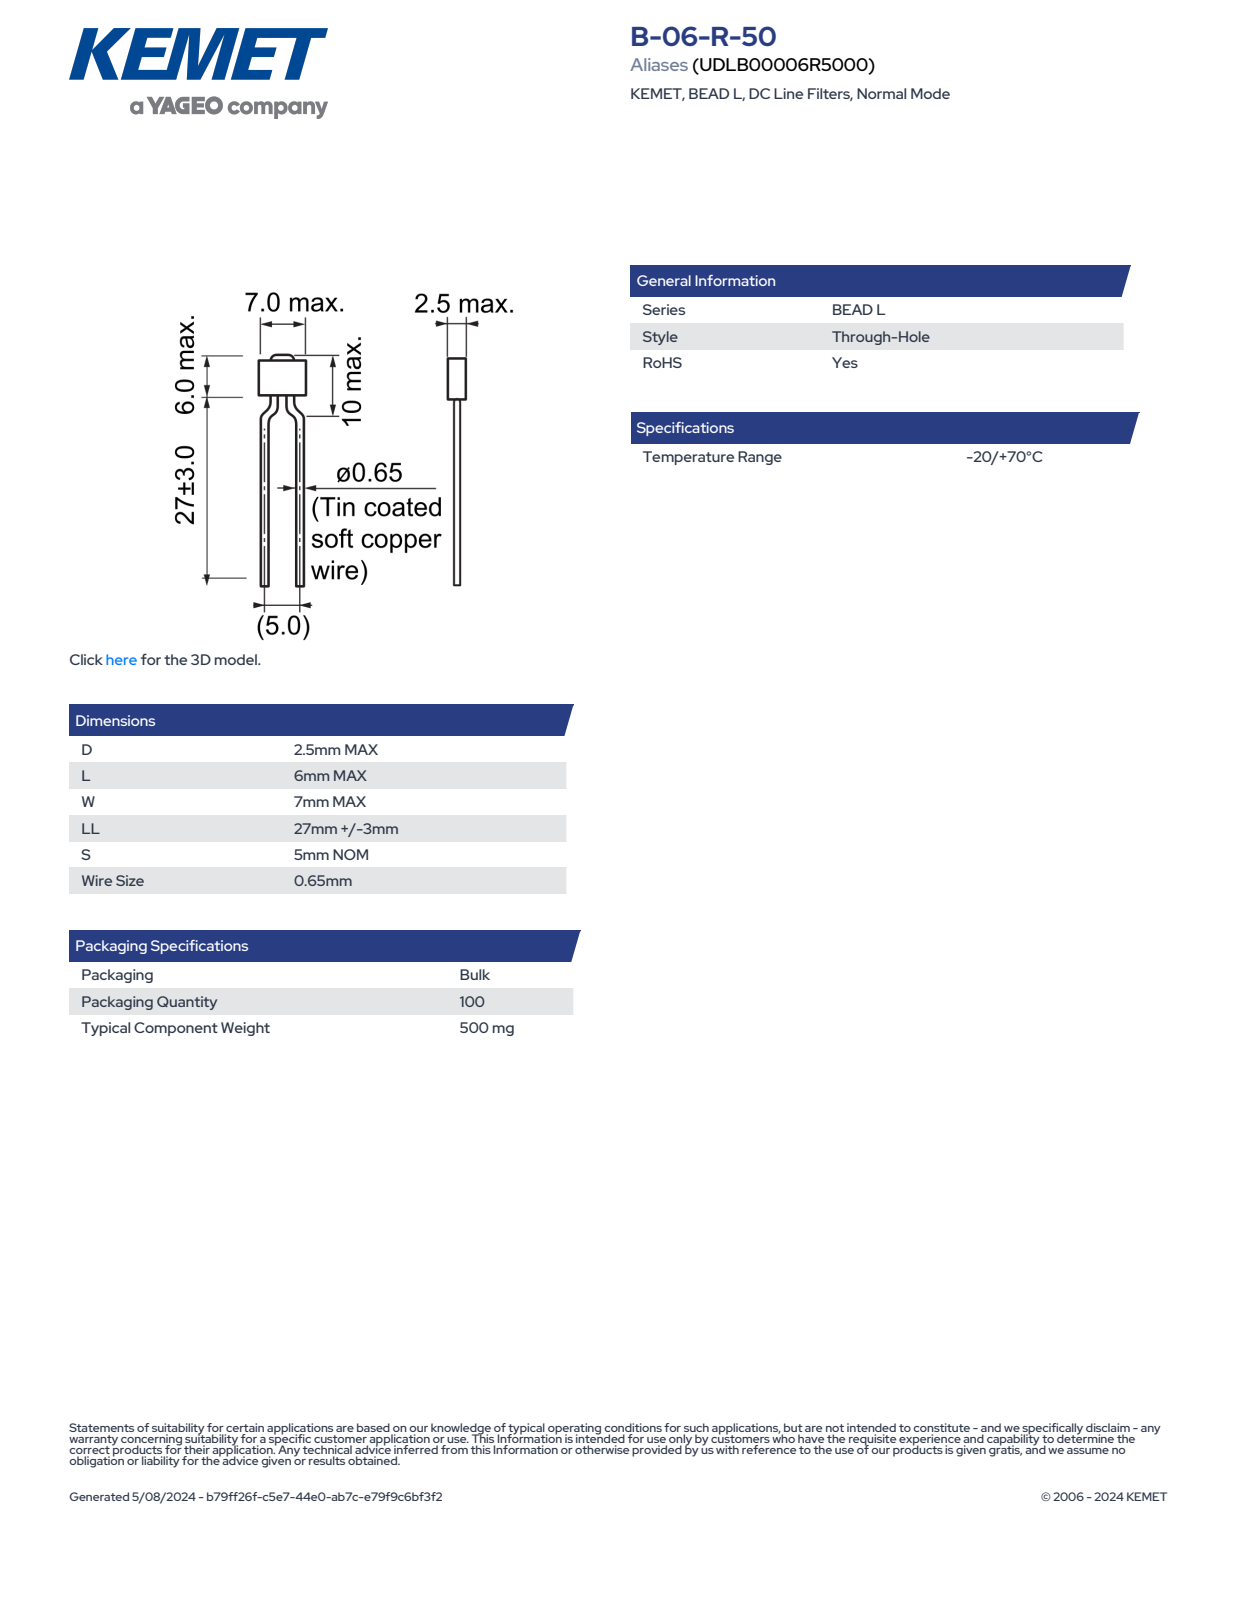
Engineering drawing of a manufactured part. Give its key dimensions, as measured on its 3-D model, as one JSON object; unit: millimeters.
{"part_name": "IL_B06R50_D2.5L6W7S5LL30", "step_written_by": "SolidWorks 2014 (AUTOMOTIVE_DESIGN)", "units": "millimeters", "bodies": {"solids": 1, "faces": 93, "planar": 63, "cylindrical": 16, "other": 14}, "overall_size": [36, 7, 2.5], "volume_mm3": 110, "surface_area_mm2": 256, "round_bosses_or_shafts": [[0.65, 6]], "partial_cylinders_radius": [[1, 4]], "face_to_face_distances": [2.5, 5.35, 7, 30, 35.35, 2.27, 3.08, 0.81, 33.08, 32.27]}
